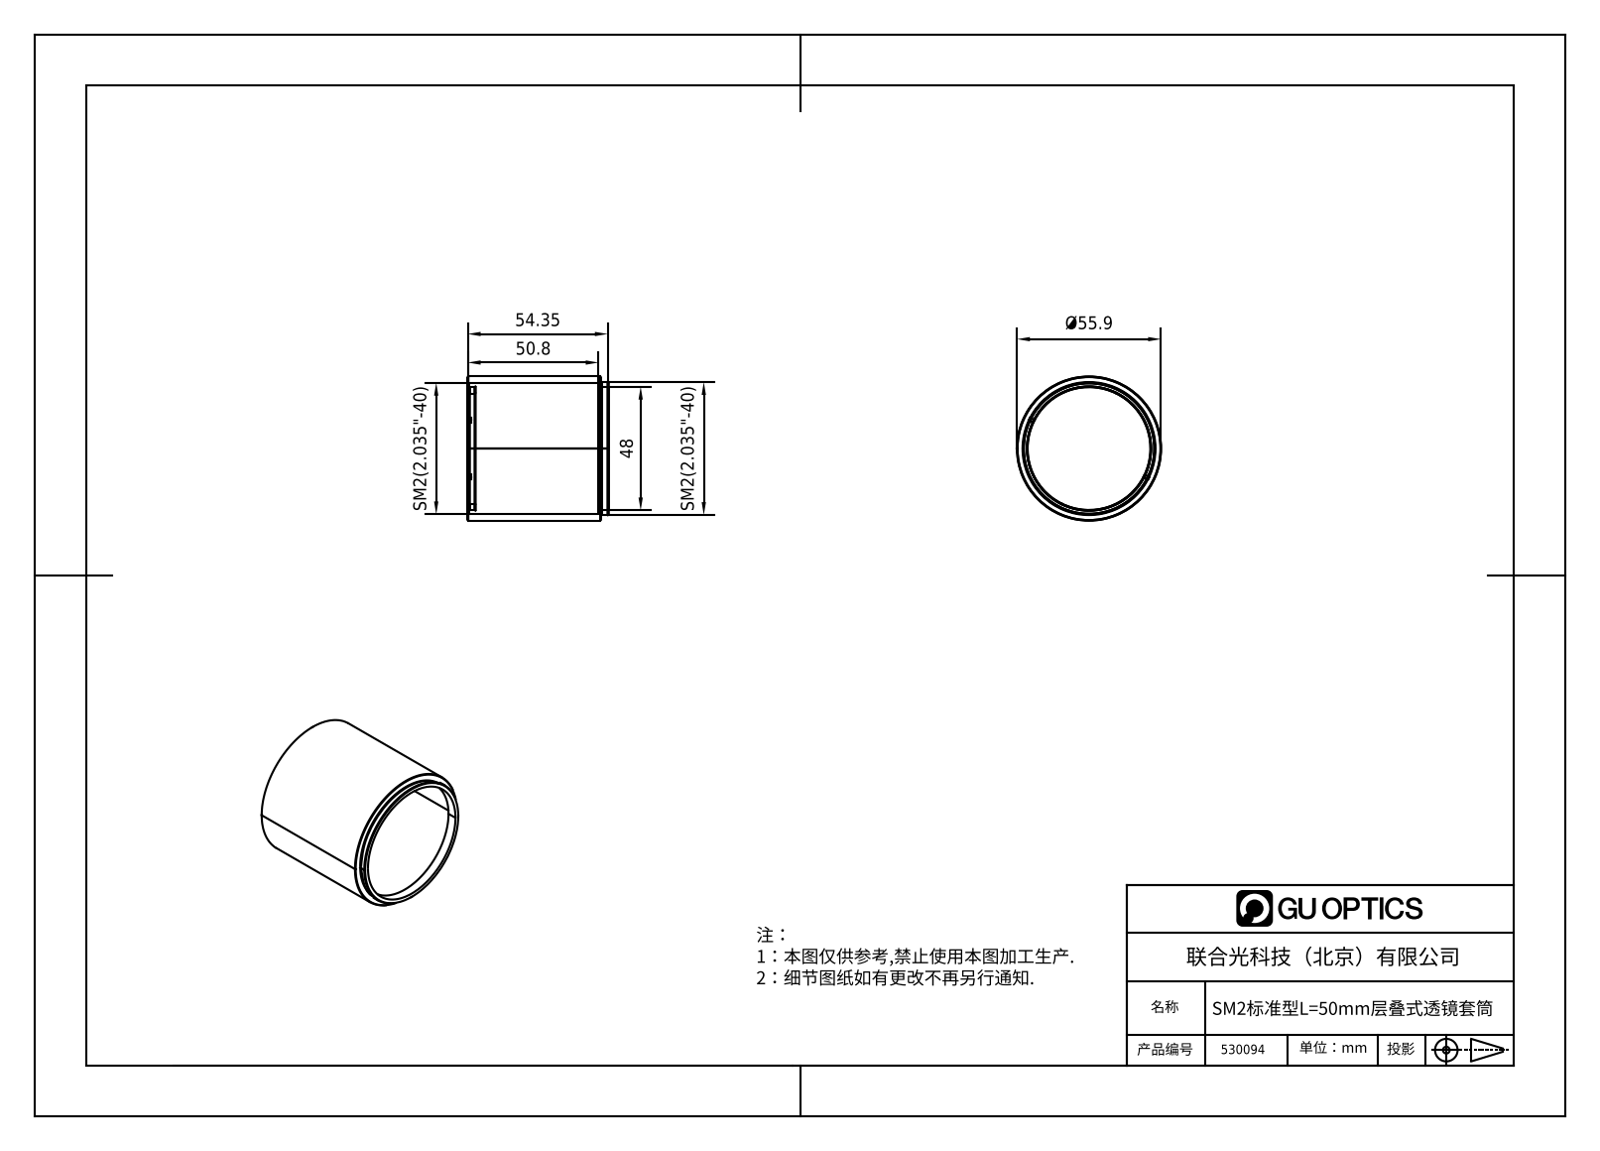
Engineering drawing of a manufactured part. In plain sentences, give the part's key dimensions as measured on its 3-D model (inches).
The part is named "1.7.1.20_ZTC-2-2.0_SM2标准型2.0英寸层叠式透镜套筒". Its 3-D file was written by "SolidWorks 2018 (AUTOMOTIVE_DESIGN)". It is 0 solids with 34 faces: 11 planar, 12 cylindrical and 11 other. Overall it measures 2.201 by 2.201 by 2.15 inches. Round holes: 1 of diameter 1.878, 1 of diameter 1.89, 1 of diameter 2.01. Round bosses or shafts: 1 of diameter 2.201, 1 of diameter 2.031, 1 of diameter 1.992. The main face-to-face distances are 2.031, 2.15, 0.118, 0.019, 2.013, 2.131, 0.046, 0.028, 1.985, 2.103.
